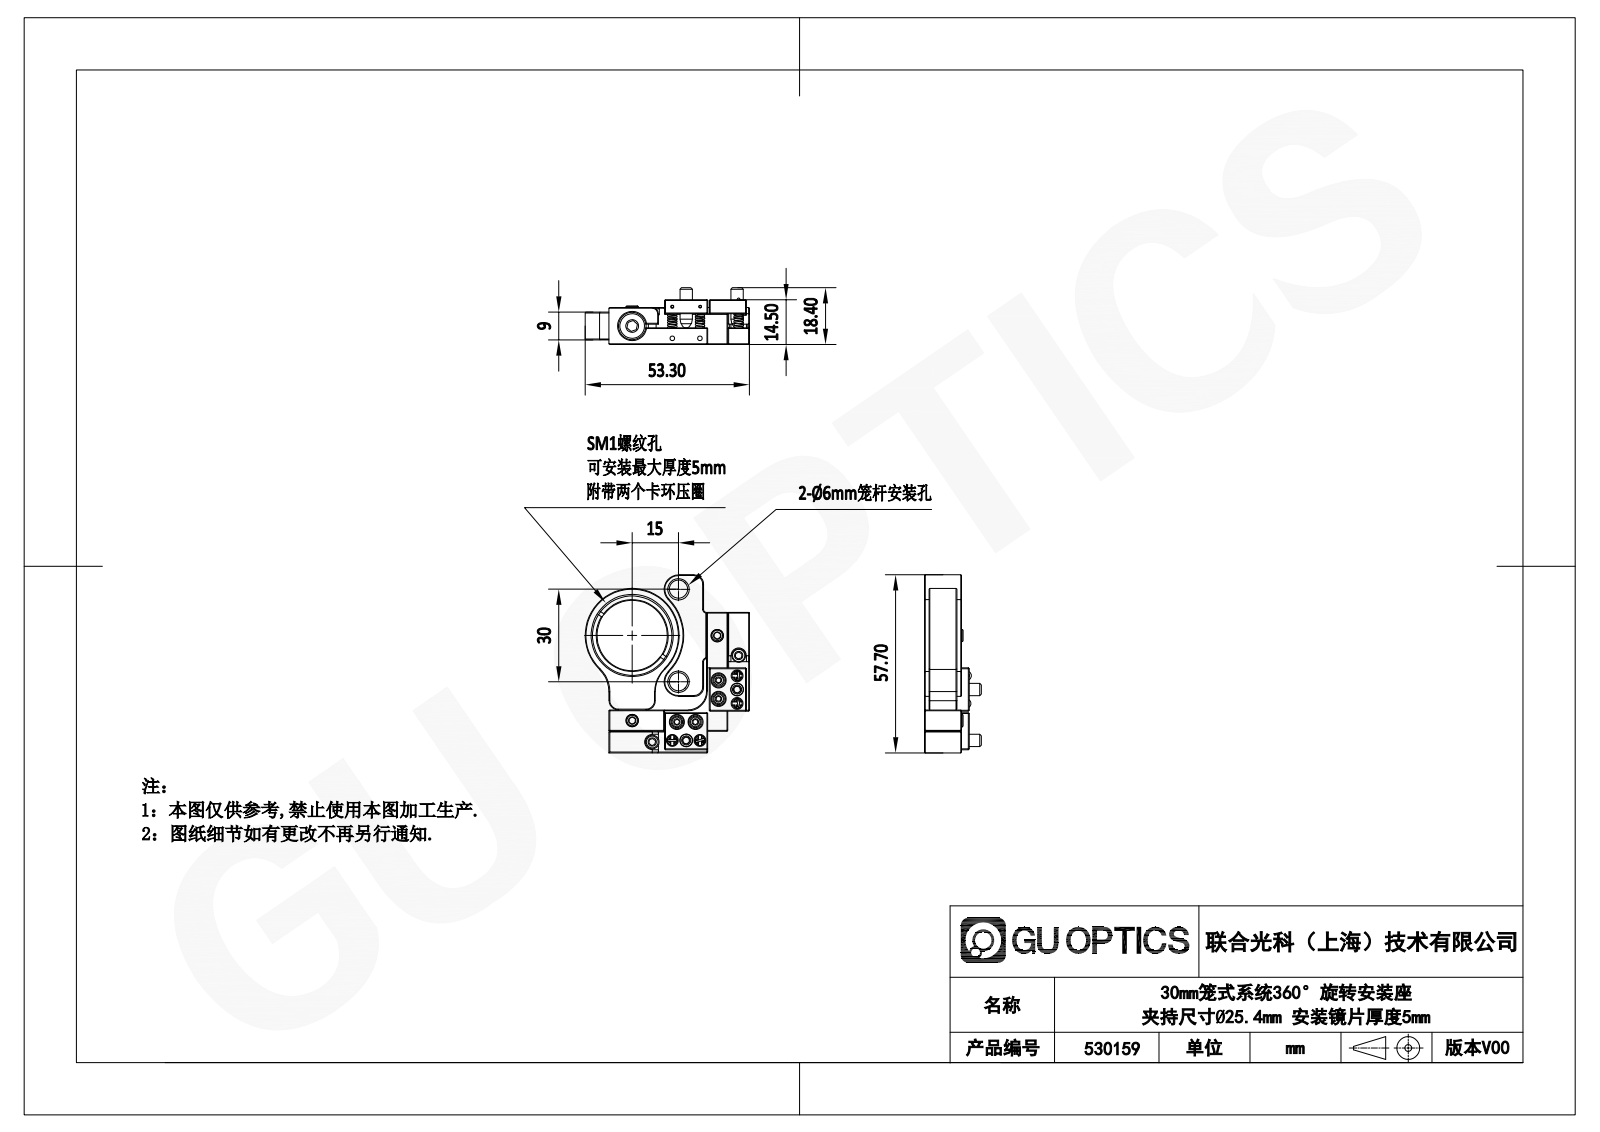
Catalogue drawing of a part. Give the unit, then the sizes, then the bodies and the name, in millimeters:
Units: millimetres
Overall size (bounding box): 57.71 × 53.25 × 18.4
Round holes (diameter × count): ⌀1 ×8, ⌀3.4 ×8, ⌀1.6 ×4, ⌀2.4 ×4, ⌀3.3 ×4, ⌀4.5 ×4, ⌀2.05 ×2, ⌀2.5 ×2, ⌀2.9 ×2, ⌀2.99 ×2, ⌀3 ×2, ⌀3.75 ×2
Round bosses / shafts (diameter × count): ⌀4 ×6, ⌀4.6 ×4, ⌀3.8 ×4, ⌀3 ×4, ⌀2 ×4, ⌀2.5 ×2, ⌀26.29 ×1, ⌀9 ×1
Partial cylindrical surfaces — rounded edges, fillets, slot ends (radius × count): R3 ×4, R1 ×2, R2 ×2, R2.5 ×2, R4.71 ×2, R10 ×2, R6 ×1, R15.25 ×1
Main face-to-face distances: 1.5, 12, 10.5, 2, 0.5, 6.87, 7, 8.5, 6, 1
Hole centre spacings: 4.5, 4.53, 9, 0.5, 6.18, 6.67, 6.71, 7.16
Volume: 17 996 mm³ · Surface area: 16 577 mm²
Bodies: 38 solids, 718 faces (408 planar, 122 cylindrical, 188 other)
Part name (STEP PRODUCT): 530159
STEP written by: SolidWorks 2020 (CONFIG_CONTROL_DESIGN)
